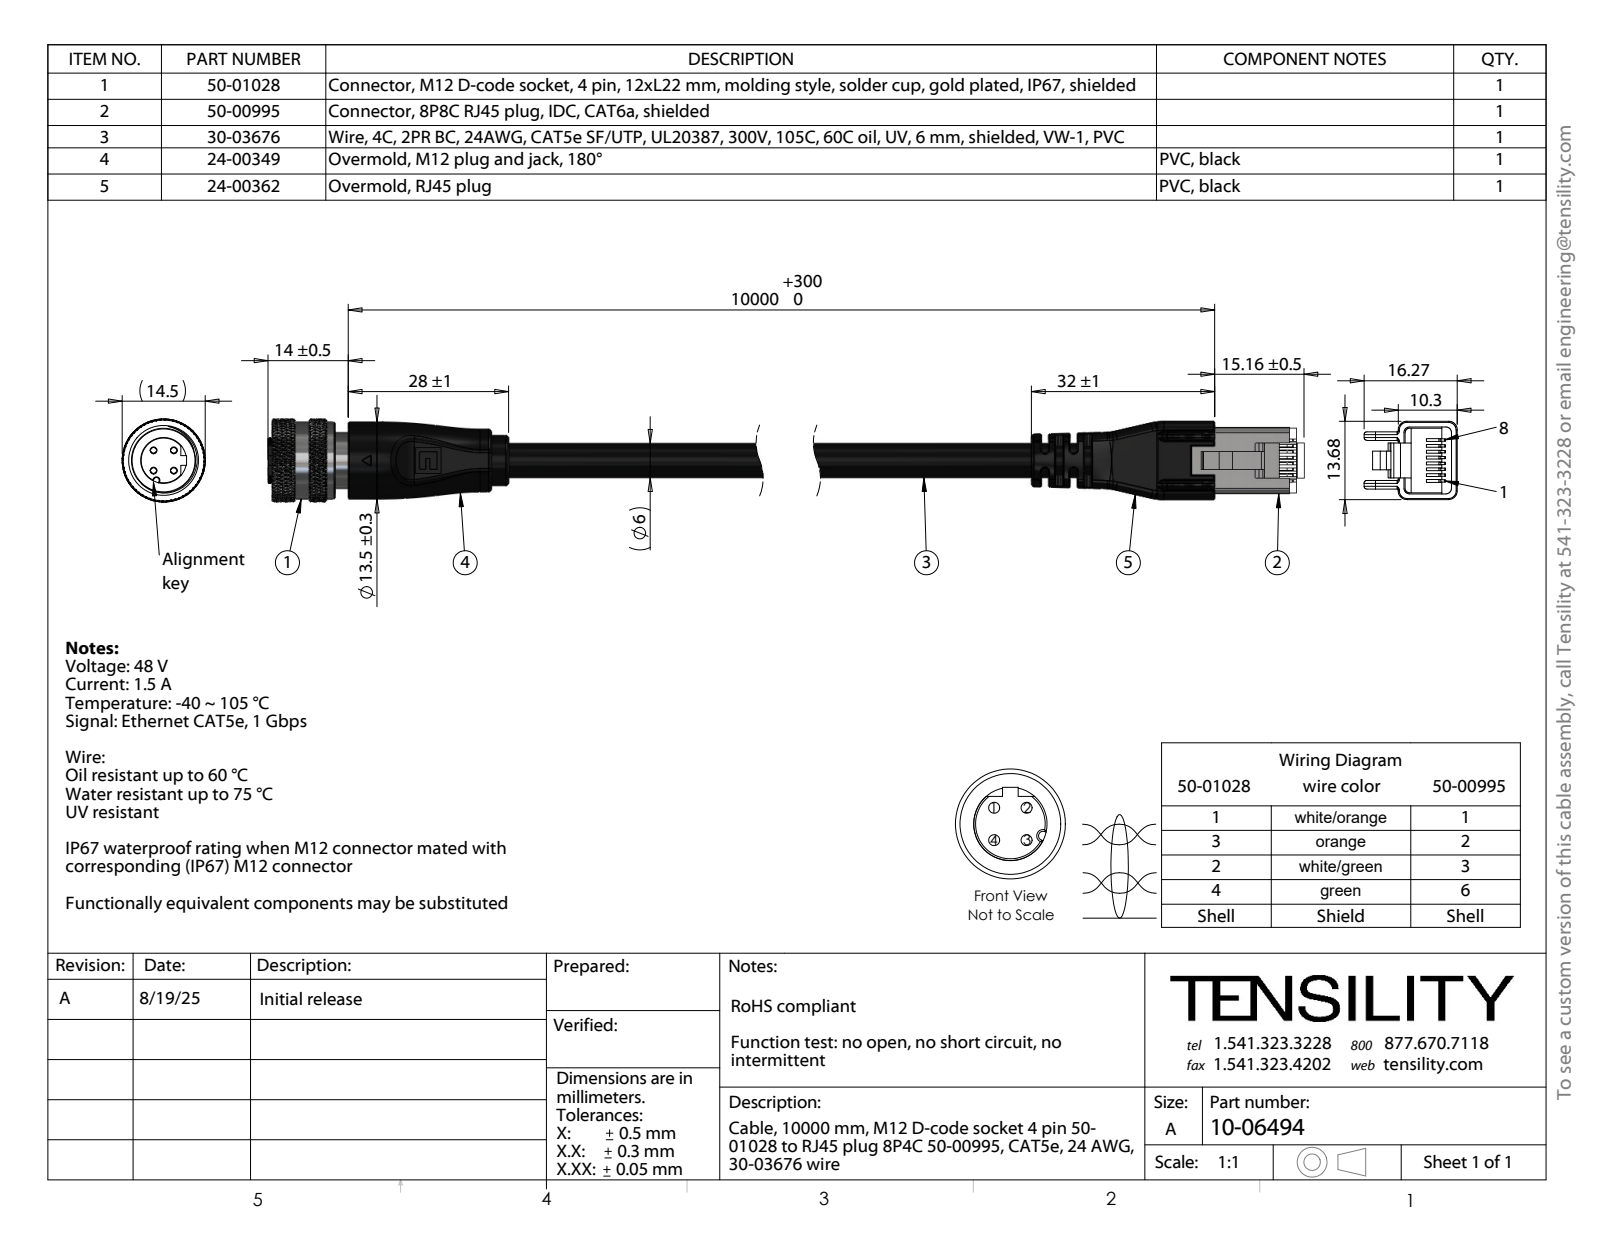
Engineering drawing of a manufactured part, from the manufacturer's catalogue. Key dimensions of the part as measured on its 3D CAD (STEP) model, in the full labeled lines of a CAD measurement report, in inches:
Part name (STEP PRODUCT): 50-01028-02_默认; 50-01028-05_默认; 50-01028-03_默认; 50-00995 (+7 more)
STEP written by: SolidWorks 2025 (CONFIG_CONTROL_DESIGN)
Units: inches
Bodies: 55 solids, 3967 faces (546 planar, 928 cylindrical, 2493 other)
Overall size (bounding box): 9.02 × 0.723 × 0.571
Volume: 0.869 in³ · Surface area: 46.04 in²
Round holes (diameter × count): ⌀0.008 ×28, ⌀0.041 ×4, ⌀0.043 ×4, ⌀0.047 ×4, ⌀0.124 ×1, ⌀0.126 ×1, ⌀0.14 ×1, ⌀0.354 ×1, ⌀0.394 ×1, ⌀0.441 ×1
Round bosses / shafts (diameter × count): ⌀0.063 ×4, ⌀0.059 ×4, ⌀0.531 ×1, ⌀0.433 ×1, ⌀0.417 ×1, ⌀0.413 ×1, ⌀0.386 ×1, ⌀0.382 ×1
Partial cylindrical surfaces — rounded edges, fillets, slot ends (radius × count): R0.008 ×11, R0.004 ×10, R0.02 ×10, R0.059 ×10, R0.024 ×8, R0.016 ×6, R0.039 ×5, R0.394 ×4
Main face-to-face distances: 0.049, 0.039, 0.098, 0.148, 0.366, 0.197, 0.059, 7.854, 0.499, 0.335
Hole centre spacings: 0.075, 0.014, 0.082, 0.042, 0.035, 0.043, 0.049, 0.071
